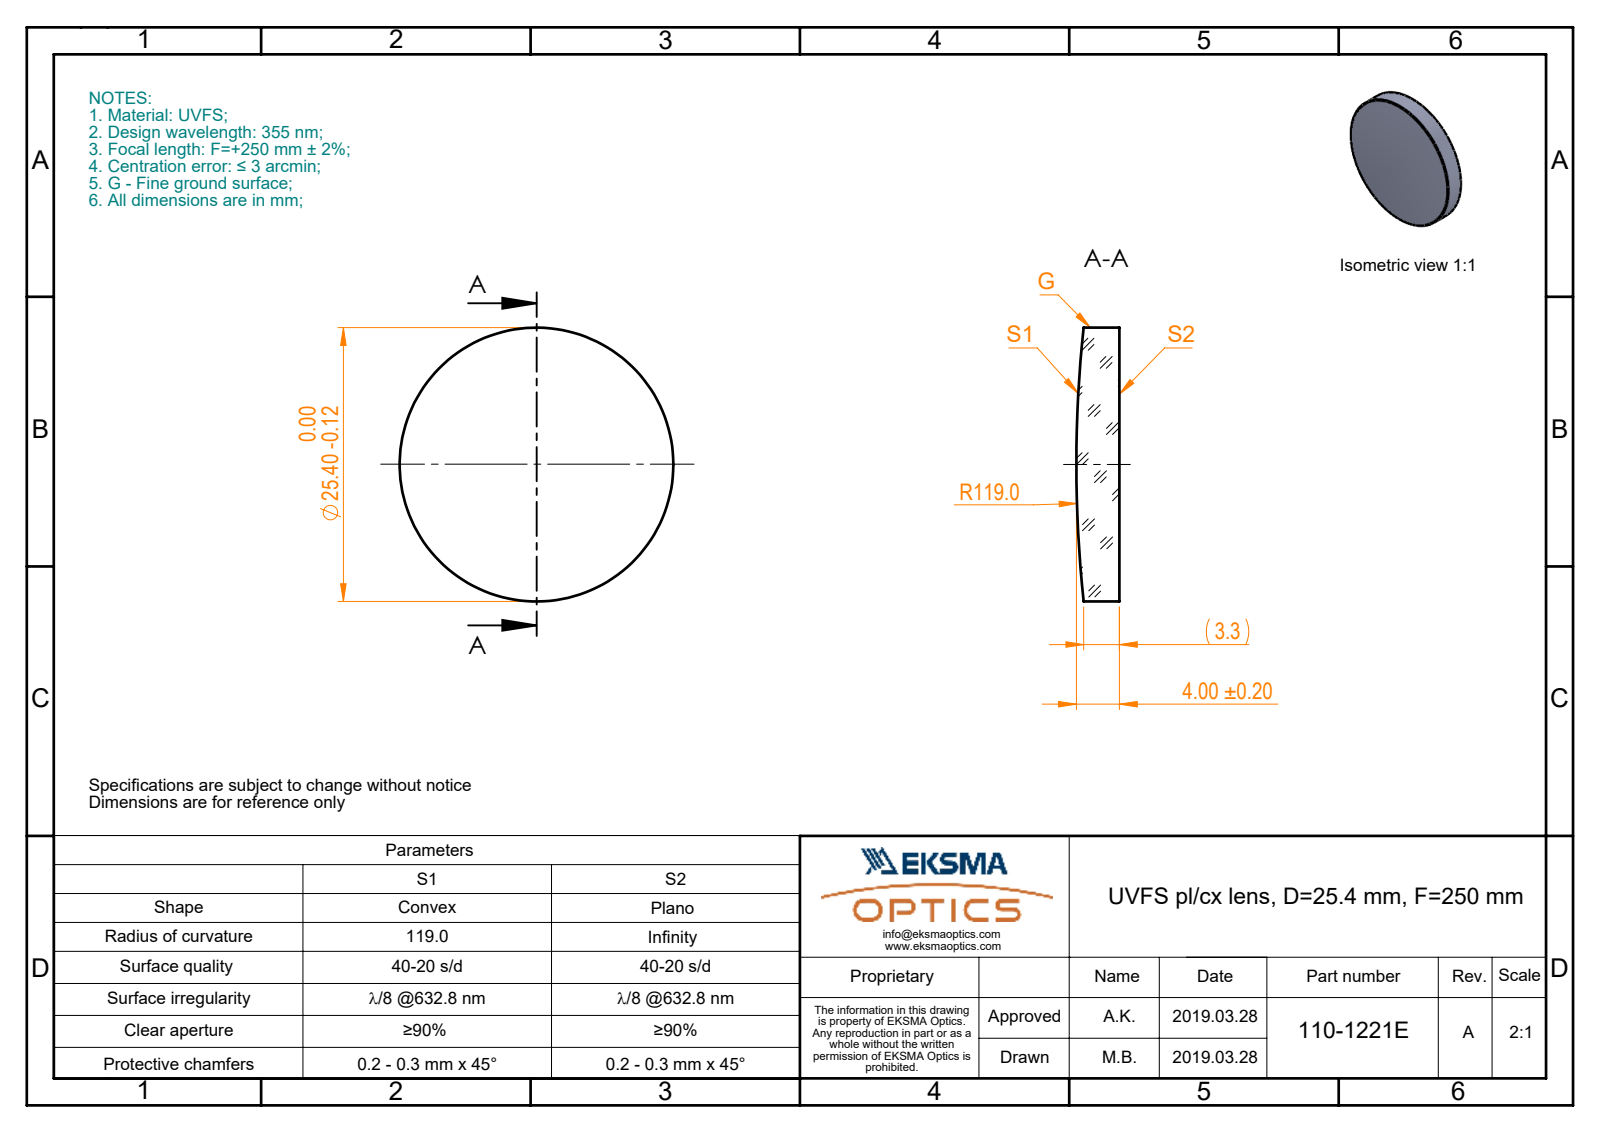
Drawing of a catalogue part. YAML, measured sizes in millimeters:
part_name: "110-1221E UVFS pl-cx 25.4 F250"
step_written_by: "SolidWorks 2017 (CONFIG_CONTROL_DESIGN)"
units: millimeters
bodies: {solids: 1, faces: 5, planar: 1, cylindrical: 2, other: 2}
overall_size: [25.4, 25.4, 4]
volume: 1855
surface_area: 1280
round_bosses_or_shafts:
  - {diameter: 25.4, count: 1}
